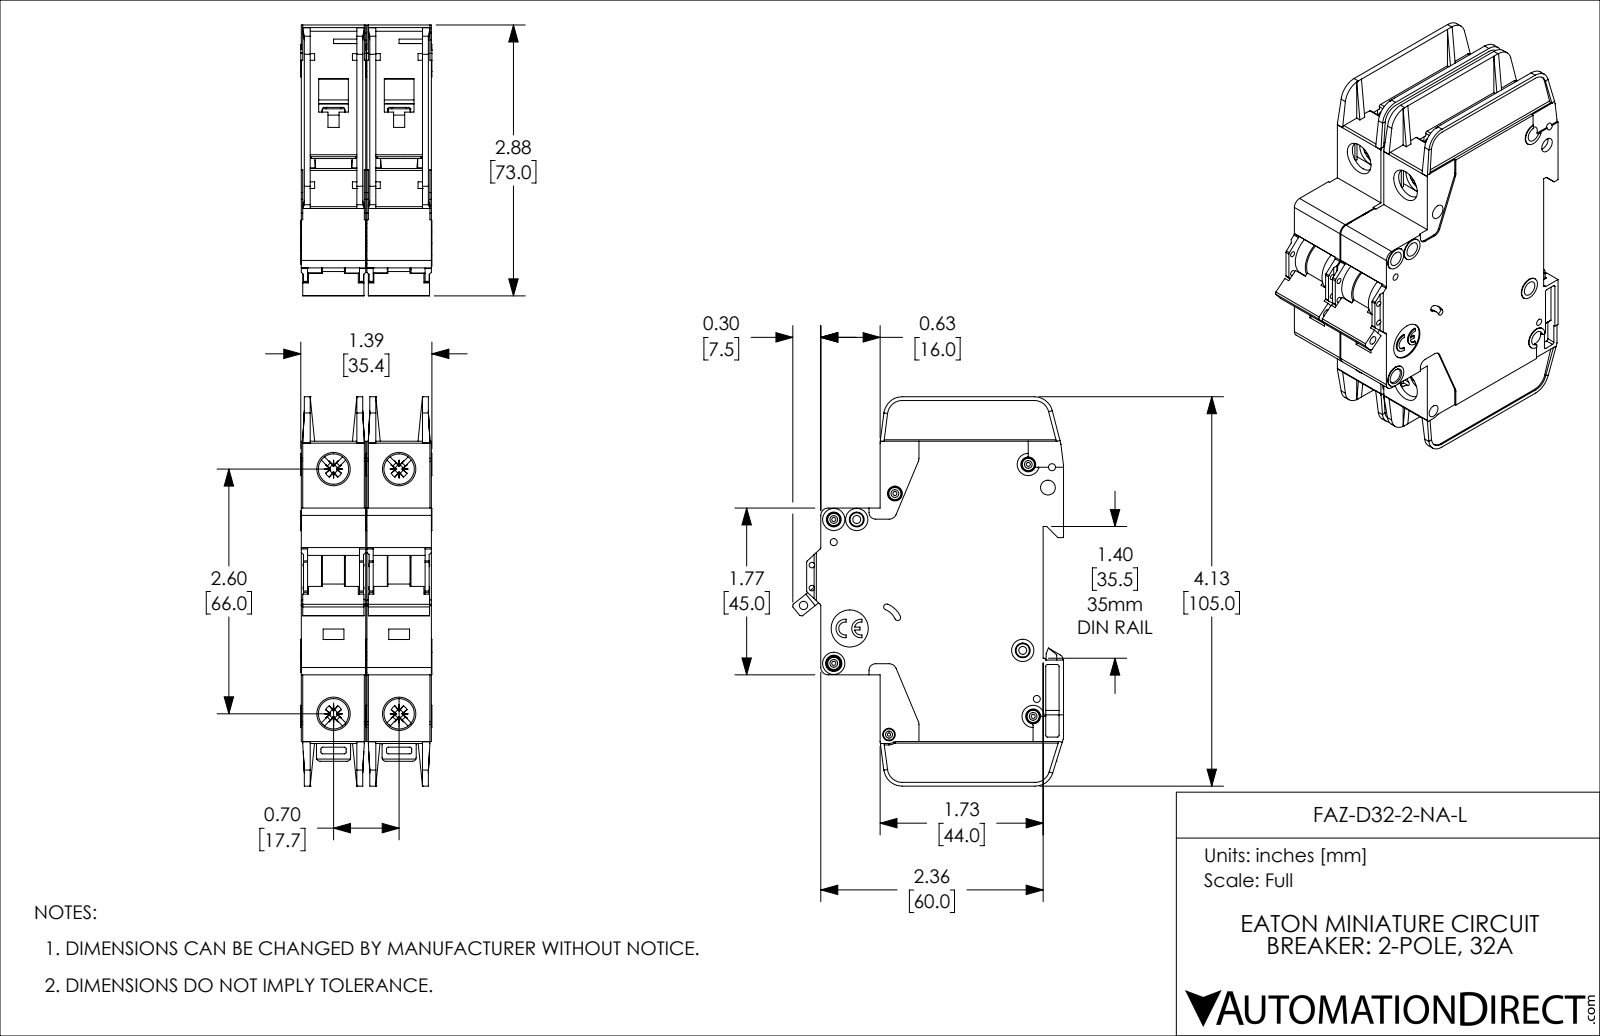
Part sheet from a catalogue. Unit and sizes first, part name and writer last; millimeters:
Units: millimetres
Overall size (bounding box): 105 × 73.1 × 35.4
Round holes (diameter × count): ⌀4 ×8, ⌀1.1 ×5, ⌀1.9 ×4, ⌀8.2 ×4, ⌀1.5 ×2, ⌀2.2 ×2, ⌀0.9 ×1, ⌀2.3 ×1, ⌀2.5 ×1, ⌀3.4 ×1, ⌀10 ×1
Round bosses / shafts (diameter × count): ⌀3.3 ×5, ⌀6 ×4, ⌀3 ×3, ⌀2.5 ×2
Partial cylindrical surfaces — rounded edges, fillets, slot ends (radius × count): R0.5 ×57, R0.4 ×20, R1 ×14, R2 ×10, R1.1 ×8, R0.2 ×5, R5 ×5, R0.3 ×4
Main face-to-face distances: 17.7, 1.2, 17.4, 15, 2.4, 16.2, 13.8, 35.1, 18.9, 16.5
Hole centre spacings: 6.2, 13.6, 17.7, 22.1, 66, 68.3, 4.8, 5.1
Volume: 153 500 mm³ · Surface area: 52 910 mm²
Bodies: 2 solids, 2254 faces (1342 planar, 714 cylindrical, 198 other)
Part name (STEP PRODUCT): FAZ-D32-2-NA-L
STEP written by: SolidWorks 2019 (AUTOMOTIVE_DESIGN)
